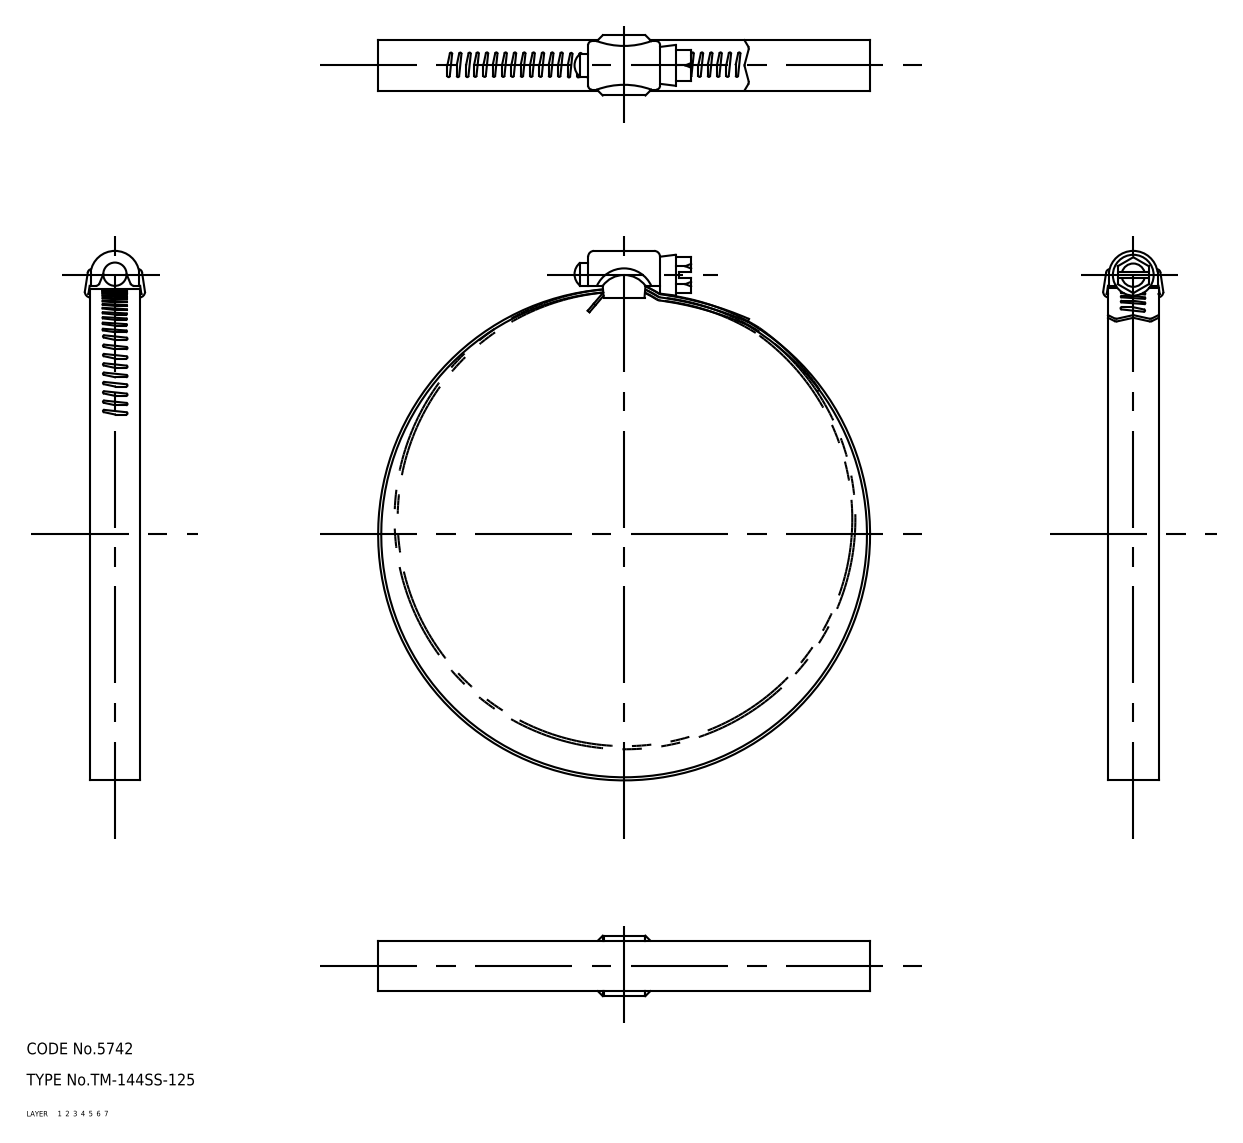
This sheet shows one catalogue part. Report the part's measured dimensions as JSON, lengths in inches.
{"part_name": "screw; holder; band; TM_144SS_125_19446_36", "step_written_by": "CADfix (AUTOMOTIVE_DESIGN)", "units": "inches", "bodies": {"solids": 3, "faces": 216, "planar": 0, "cylindrical": 0, "other": 216}, "overall_size": [5.365, 4.984, 0.615], "volume_in3": 0.407, "surface_area_in2": 22.21}
